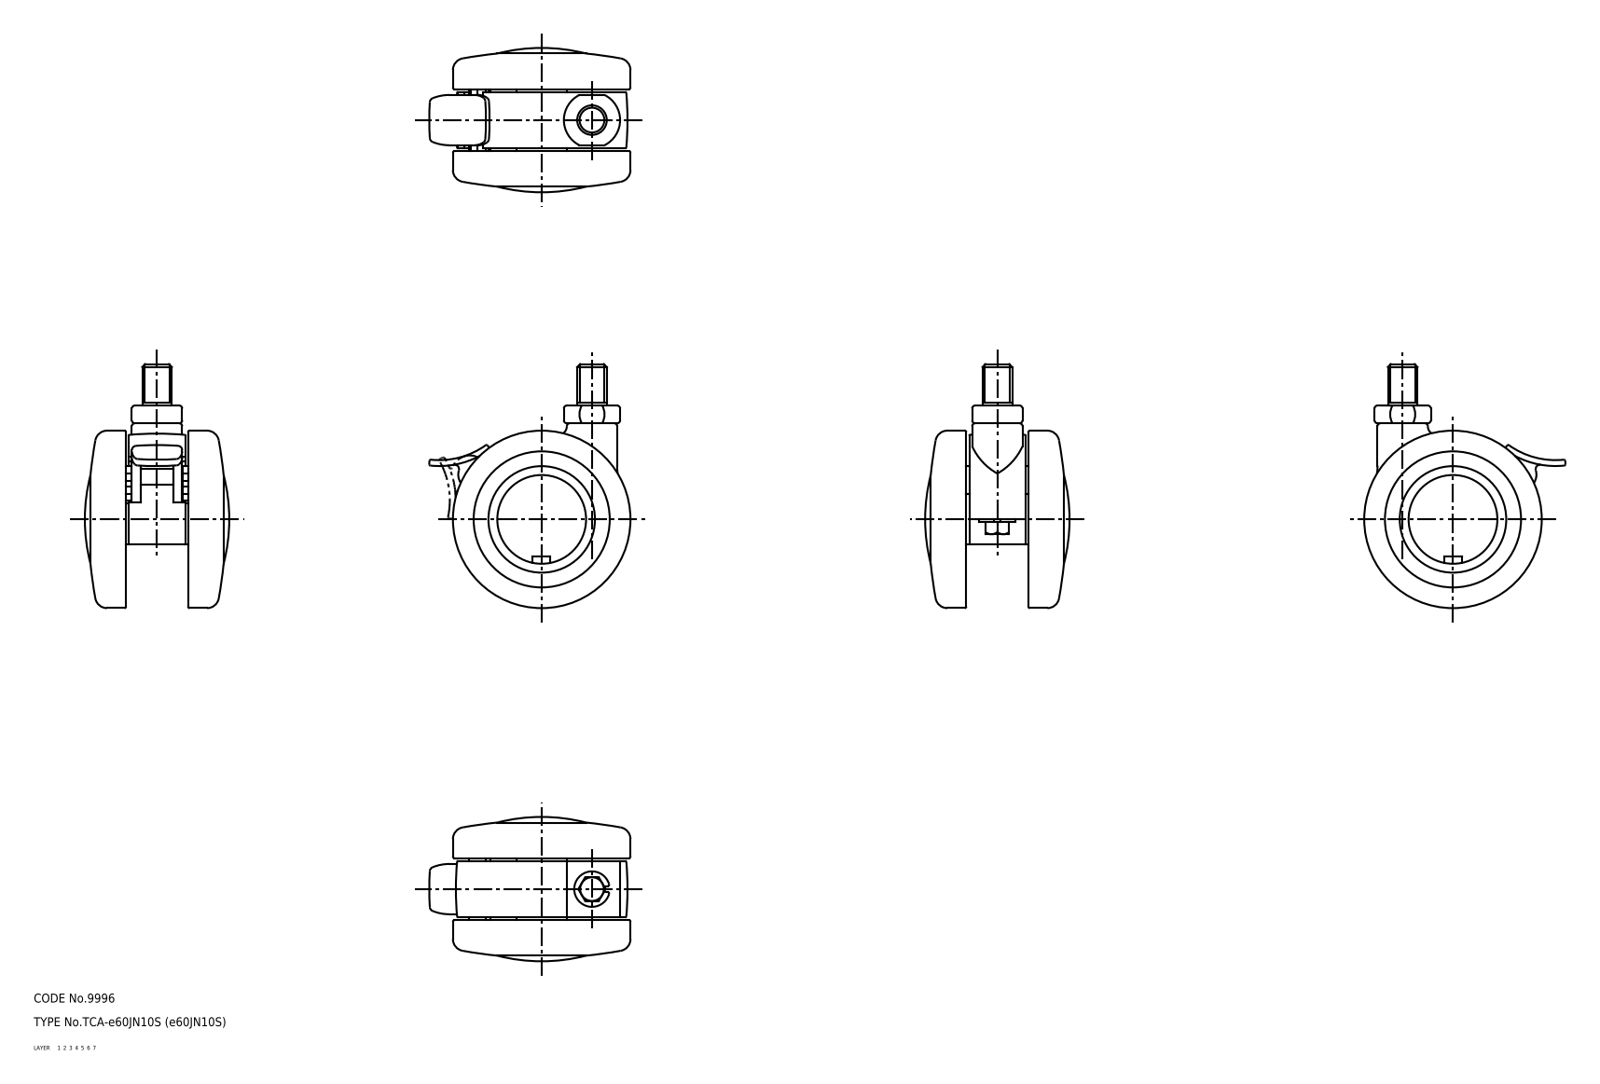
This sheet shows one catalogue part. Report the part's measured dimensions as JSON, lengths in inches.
{"part_name": "lever; wheel_mr; wheel; main shaft (+1 more)", "step_written_by": "CADfix (AUTOMOTIVE_DESIGN)", "units": "inches", "bodies": {"solids": 5, "faces": 208, "planar": 0, "cylindrical": 0, "other": 208}, "overall_size": [3.248, 2.677, 1.922], "volume_in3": 5.25, "surface_area_in2": 50.6}
